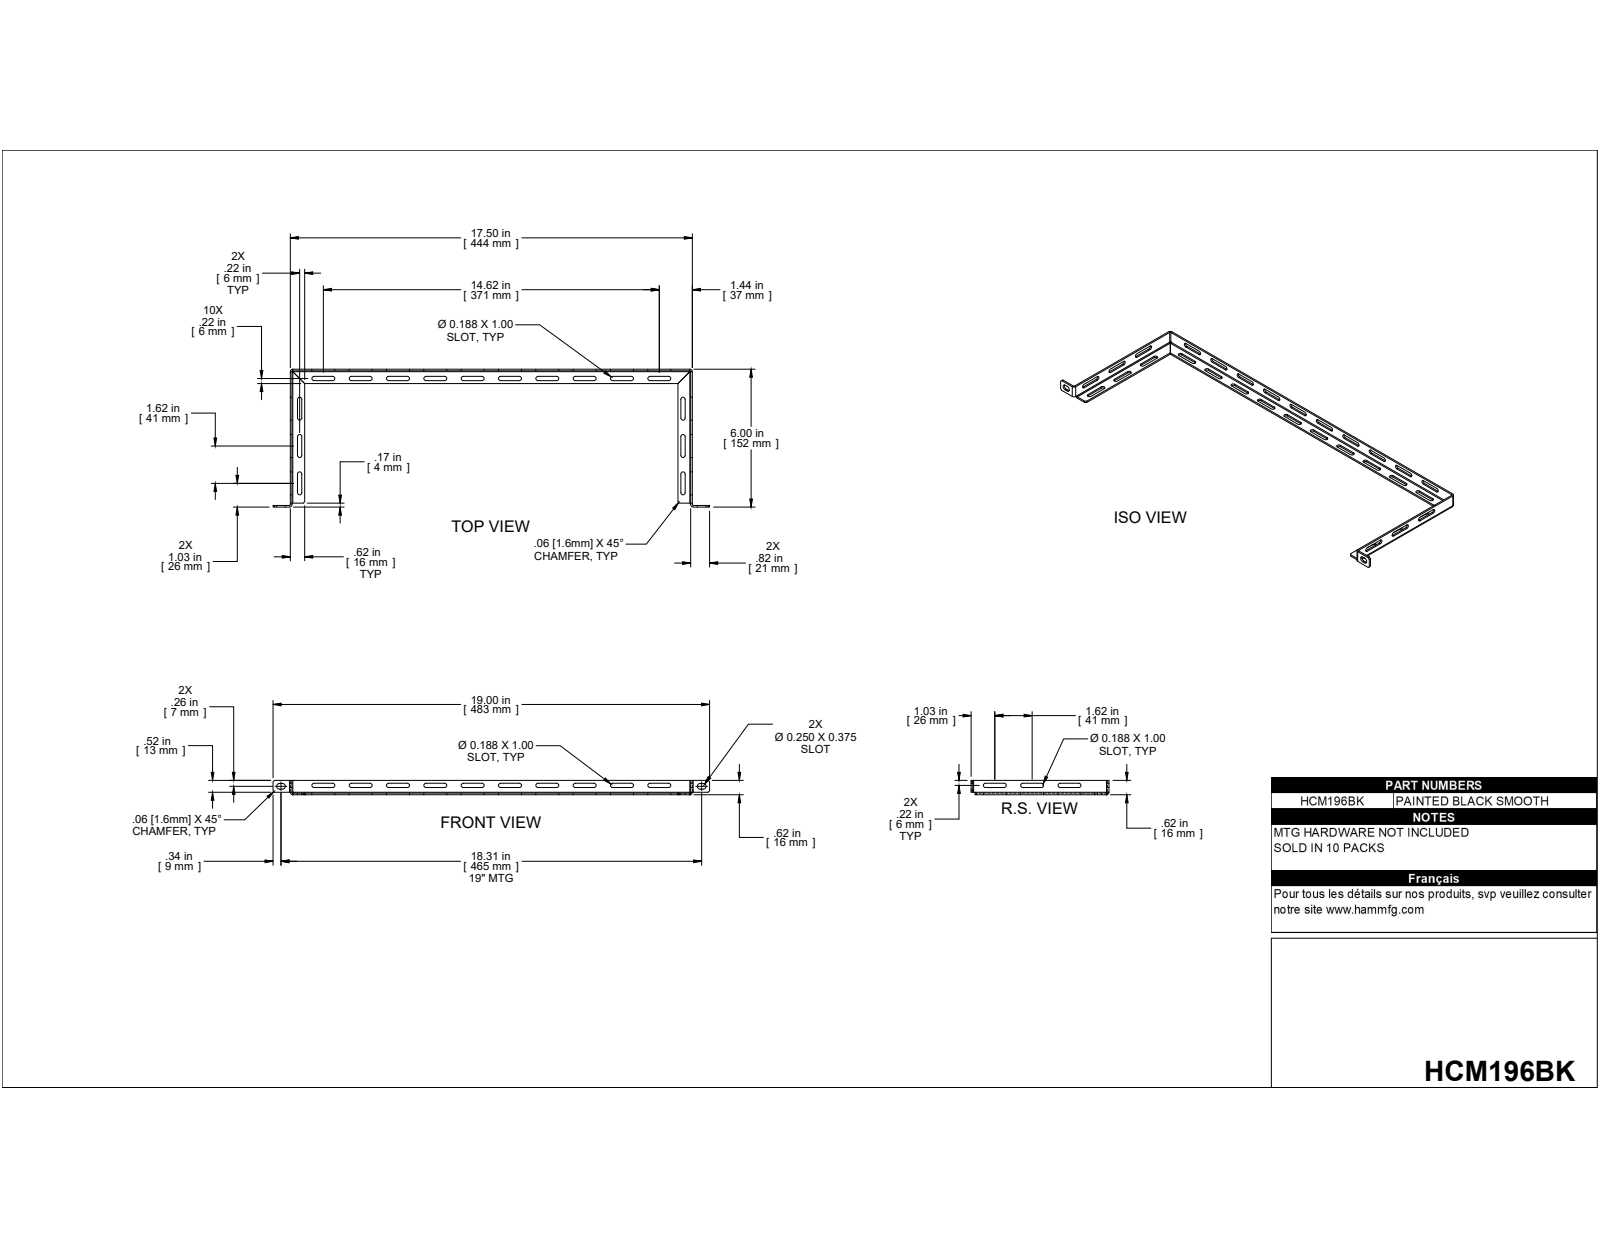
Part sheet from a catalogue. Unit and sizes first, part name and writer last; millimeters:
Units: millimetres
Overall size (bounding box): 482.6 × 152.4 × 15.88
Partial cylindrical surfaces — rounded edges, fillets, slot ends (radius × count): R2.38 ×59, R0.91 ×7, R2.74 ×7, R3.17 ×4
Main face-to-face distances: 1.83, 442.67, 14.04, 15.87, 444.5, 440.84, 7.93, 4.76, 7.94, 150.57
Volume: 32 472 mm³ · Surface area: 41 911 mm²
Bodies: 1 solid, 196 faces (110 planar, 82 cylindrical, 4 other)
Part name (STEP PRODUCT): COM57141-6
STEP written by: ST-DEVELOPER v16.7 (AUTOMOTIVE_DESIGN)
